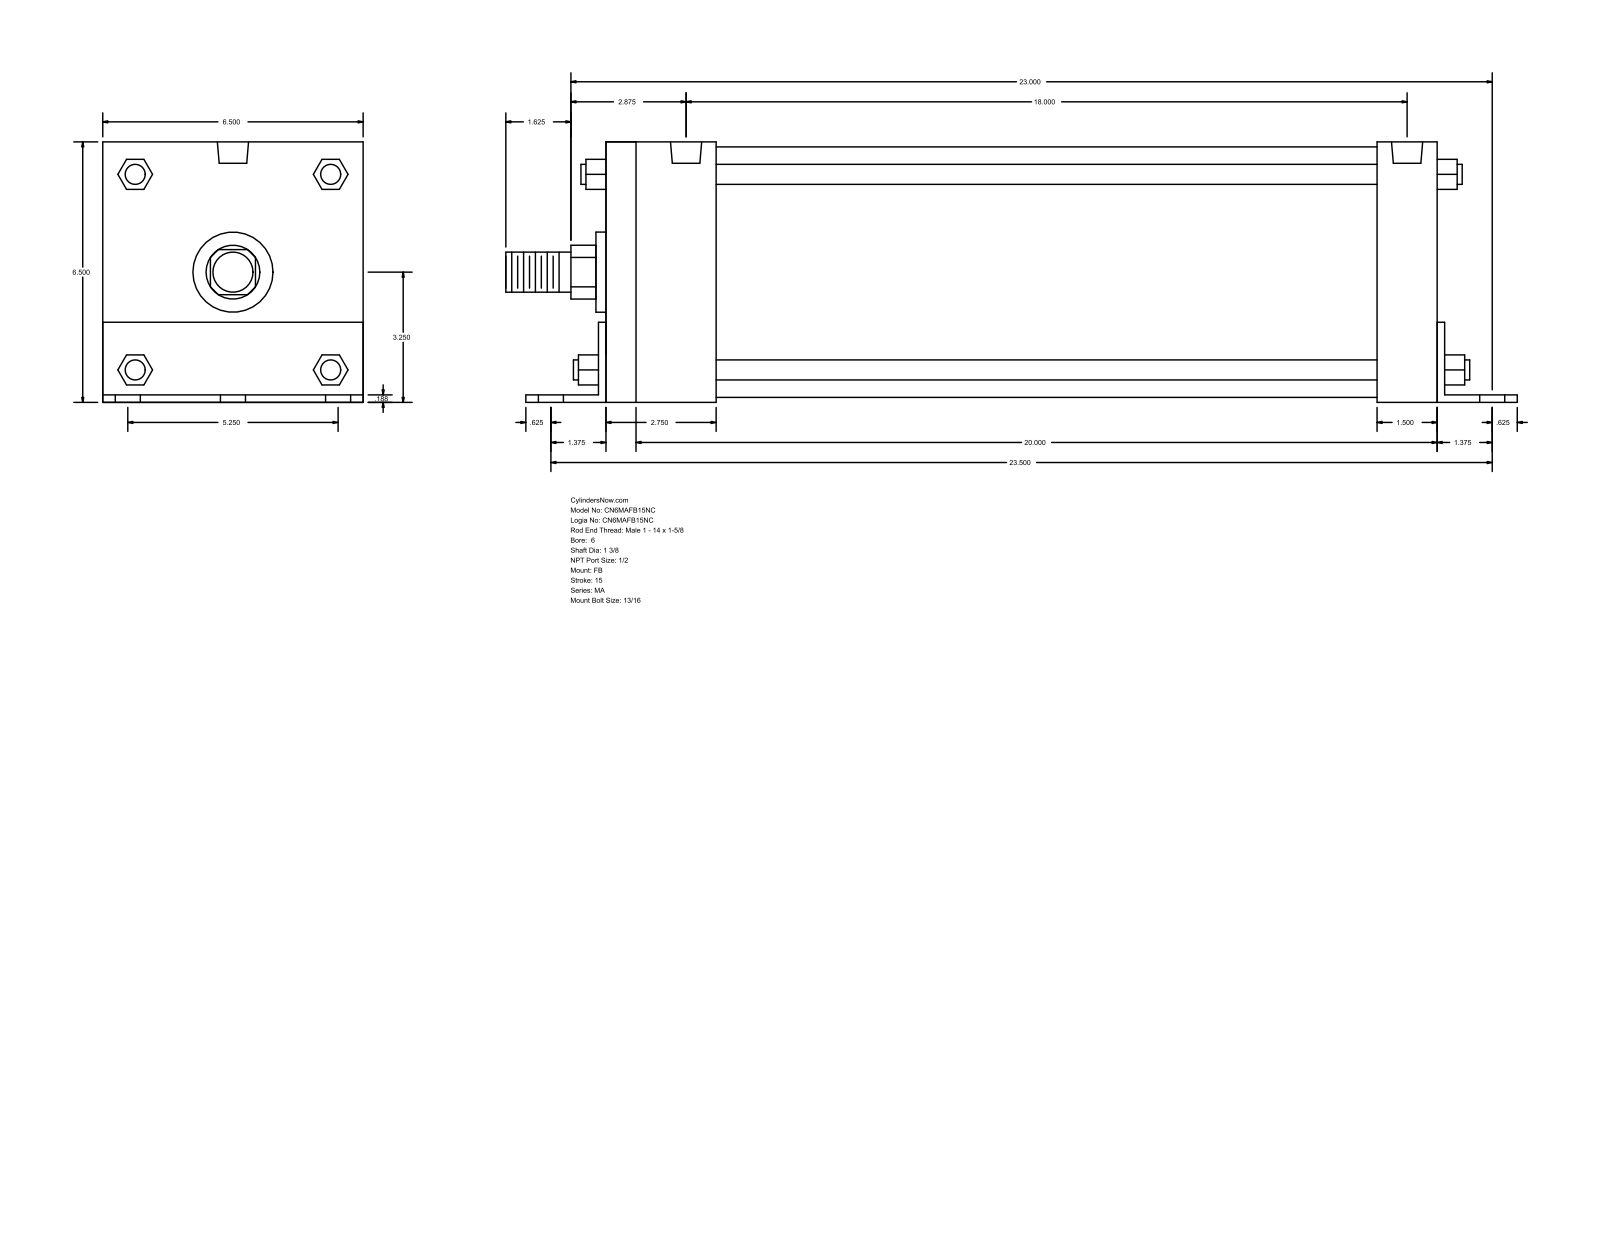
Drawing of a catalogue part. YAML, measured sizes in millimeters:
part_name: "MA_FB__0600_1.375"
step_written_by: "GSSL Pune (CONFIG_CONTROL_DESIGN)"
units: millimeters
bodies: {solids: 0, faces: 140, planar: 105, cylindrical: 35, other: 0}
overall_size: [638.17, 165.15, 165.1]
round_holes:
  - {diameter: 20.64, count: 6}
  - {diameter: 17.46, count: 4}
  - {diameter: 19.77, count: 2}
round_bosses_or_shafts:
  - {diameter: 12.7, count: 4}
  - {diameter: 158.75, count: 1}
  - {diameter: 50.8, count: 1}
  - {diameter: 34.92, count: 1}
  - {diameter: 25.4, count: 1}
partial_cylinders:
  - {radius: 17.06, count: 1}
  - {radius: 32.05, count: 1}
face_to_face_distances: [165.1, 4.76, 523.87, 165.15, 4.71, 160.39, 4.77, 38.1, 42.86, 533.4]
hole_center_spacings: [66.67, 597.45, 593.72, 83.81, 85.78, 108.6, 133.34, 454.02]
